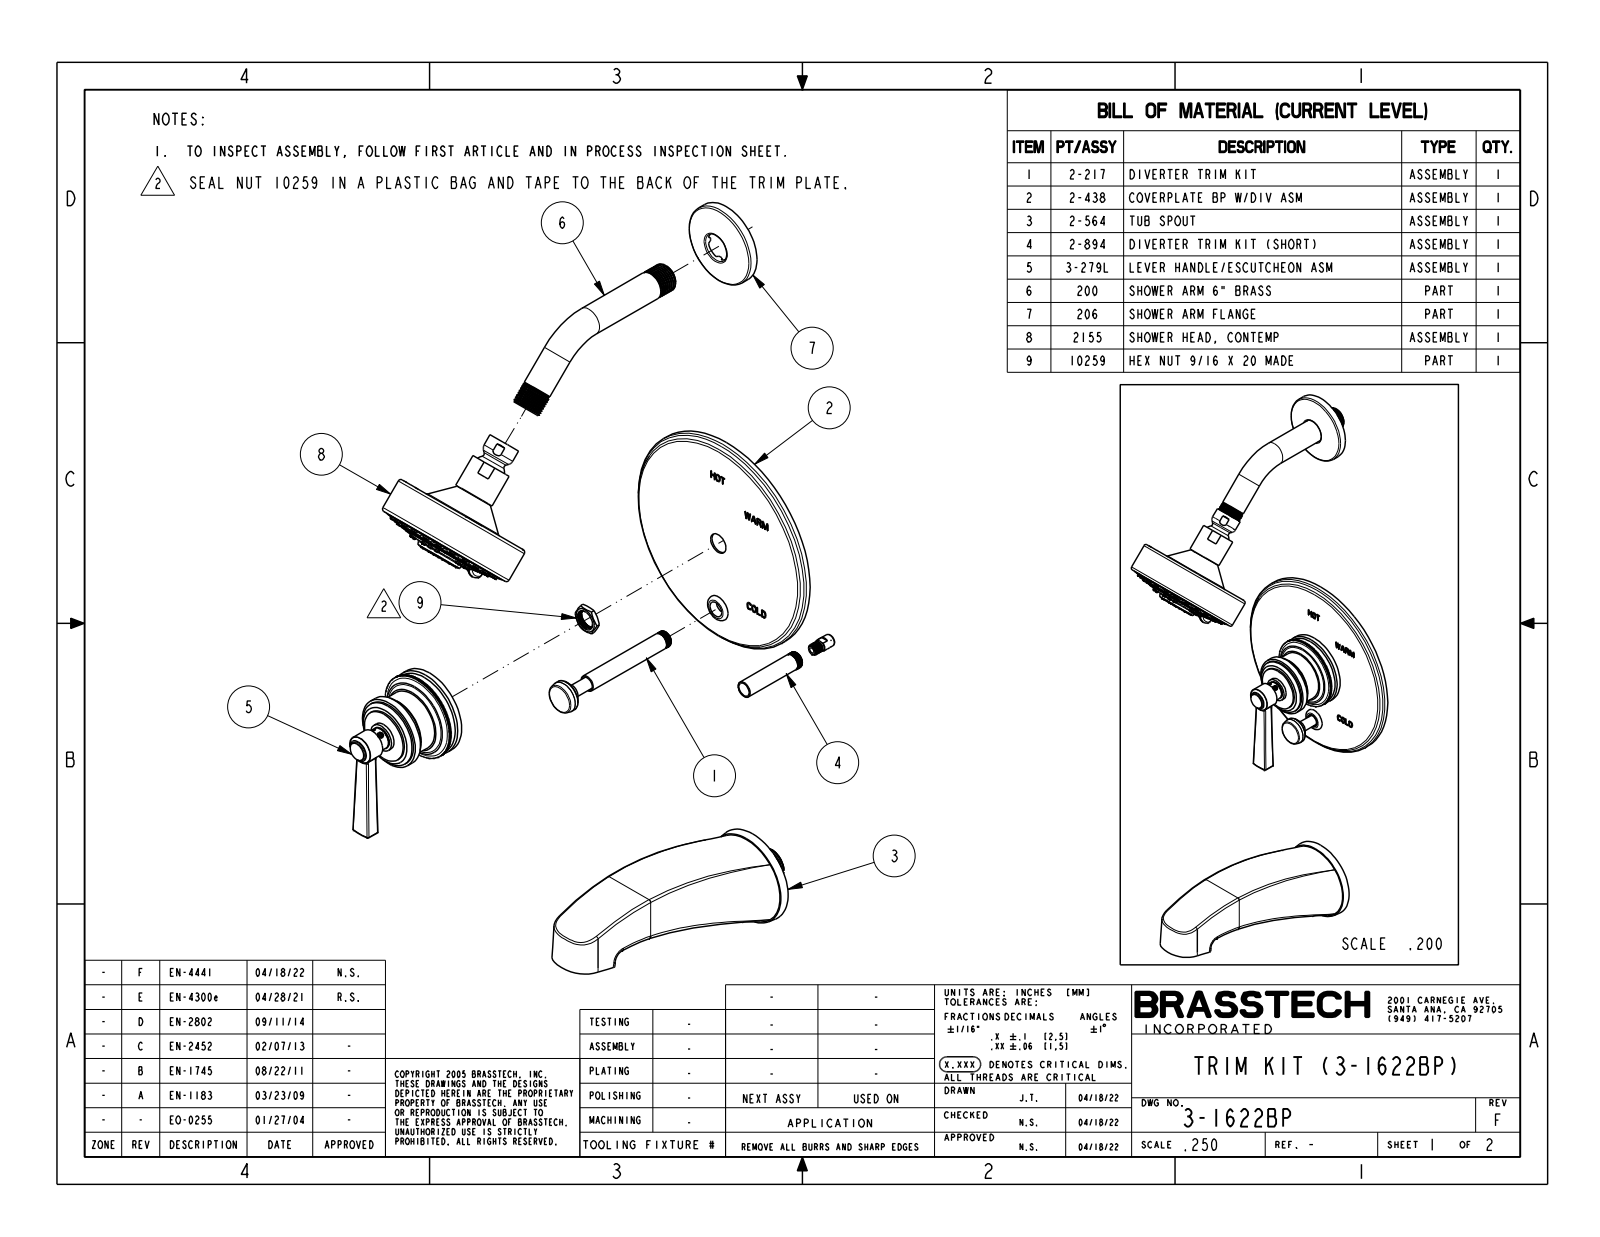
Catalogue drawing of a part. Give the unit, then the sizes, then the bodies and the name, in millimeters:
Units: millimetres
Overall size (bounding box): 547.8 × 207.6 × 165.1
Round holes (diameter × count): ⌀1.5 ×8, ⌀23.5 ×1
Round bosses / shafts (diameter × count): ⌀3.6 ×39, ⌀4.2 ×23, ⌀20.7 ×2, ⌀165.1 ×1, ⌀101.6 ×1, ⌀94.6 ×1, ⌀63.5 ×1, ⌀61 ×1
Partial cylindrical surfaces — rounded edges, fillets, slot ends (radius × count): R2 ×8, R0.5 ×2, R1 ×2, R1.4 ×2, R3.5 ×1, R12 ×1, R13 ×1, R16 ×1
Main face-to-face distances: 8, 53, 45.1, 5.1, 2.5, 29.2, 33, 3.8, 10.2, 34.9
Hole centre spacings: 11.3, 14.7, 27.2, 20.8, 20.8, 29.4, 29.4
Volume: 991 100 mm³ · Surface area: 144 100 mm²
Bodies: 3 solids, 1998 faces (776 planar, 406 cylindrical, 816 other)
Part name (STEP PRODUCT): 3-1622BP
STEP written by: CREO PARAMETRIC BY PTC INC, 2018400 (CONFIG_CONTROL_DESIGN)
